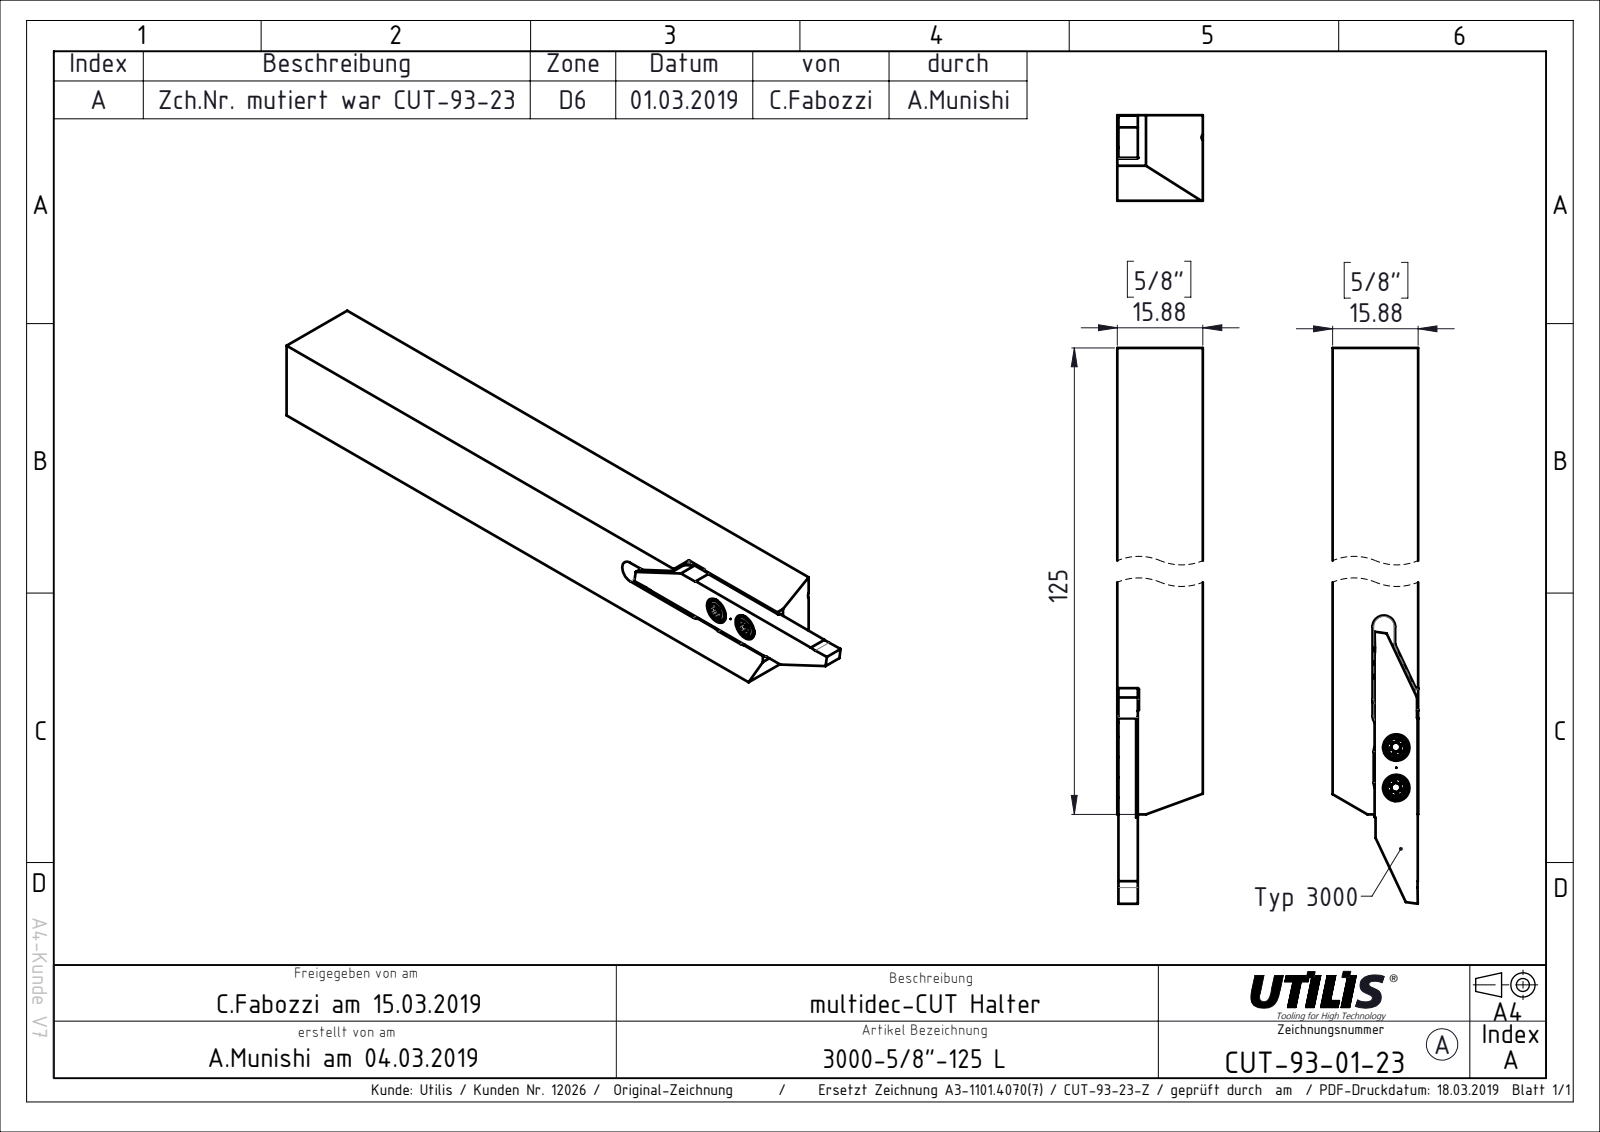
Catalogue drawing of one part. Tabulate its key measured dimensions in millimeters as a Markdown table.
| quantity | value |
| --- | --- |
| part name | CUT-Vorlage 3000 R+L Lang Kunde; CUT-93-Kunde; CUT-93-23; CUT-Vorlage 3000 R+L Lang Kunde_L-Lang (+1 more) |
| STEP written by | SolidWorks 2015 (CONFIG_CONTROL_DESIGN) |
| units | millimeters |
| bodies | 2 solids, 55 faces (36 planar, 19 cylindrical, 0 other) |
| overall size | 141.5 × 15.88 × 15.88 |
| volume | 31 018 mm³ |
| surface area | 9 638 mm² |
| round holes (diameter × count) | 2.5 × 2, 4.9 × 2 |
| partial cylindrical surfaces (radius × count) | 2.1 × 4, 0.15 × 2, 10 × 2 |
| main face-to-face distances | 15.88, 3.8, 12.08, 3.6, 15.68, 7.88, 8, 7.43, 0.45, 8.45 |
| hole center spacings | 3.75, 7.5 |
